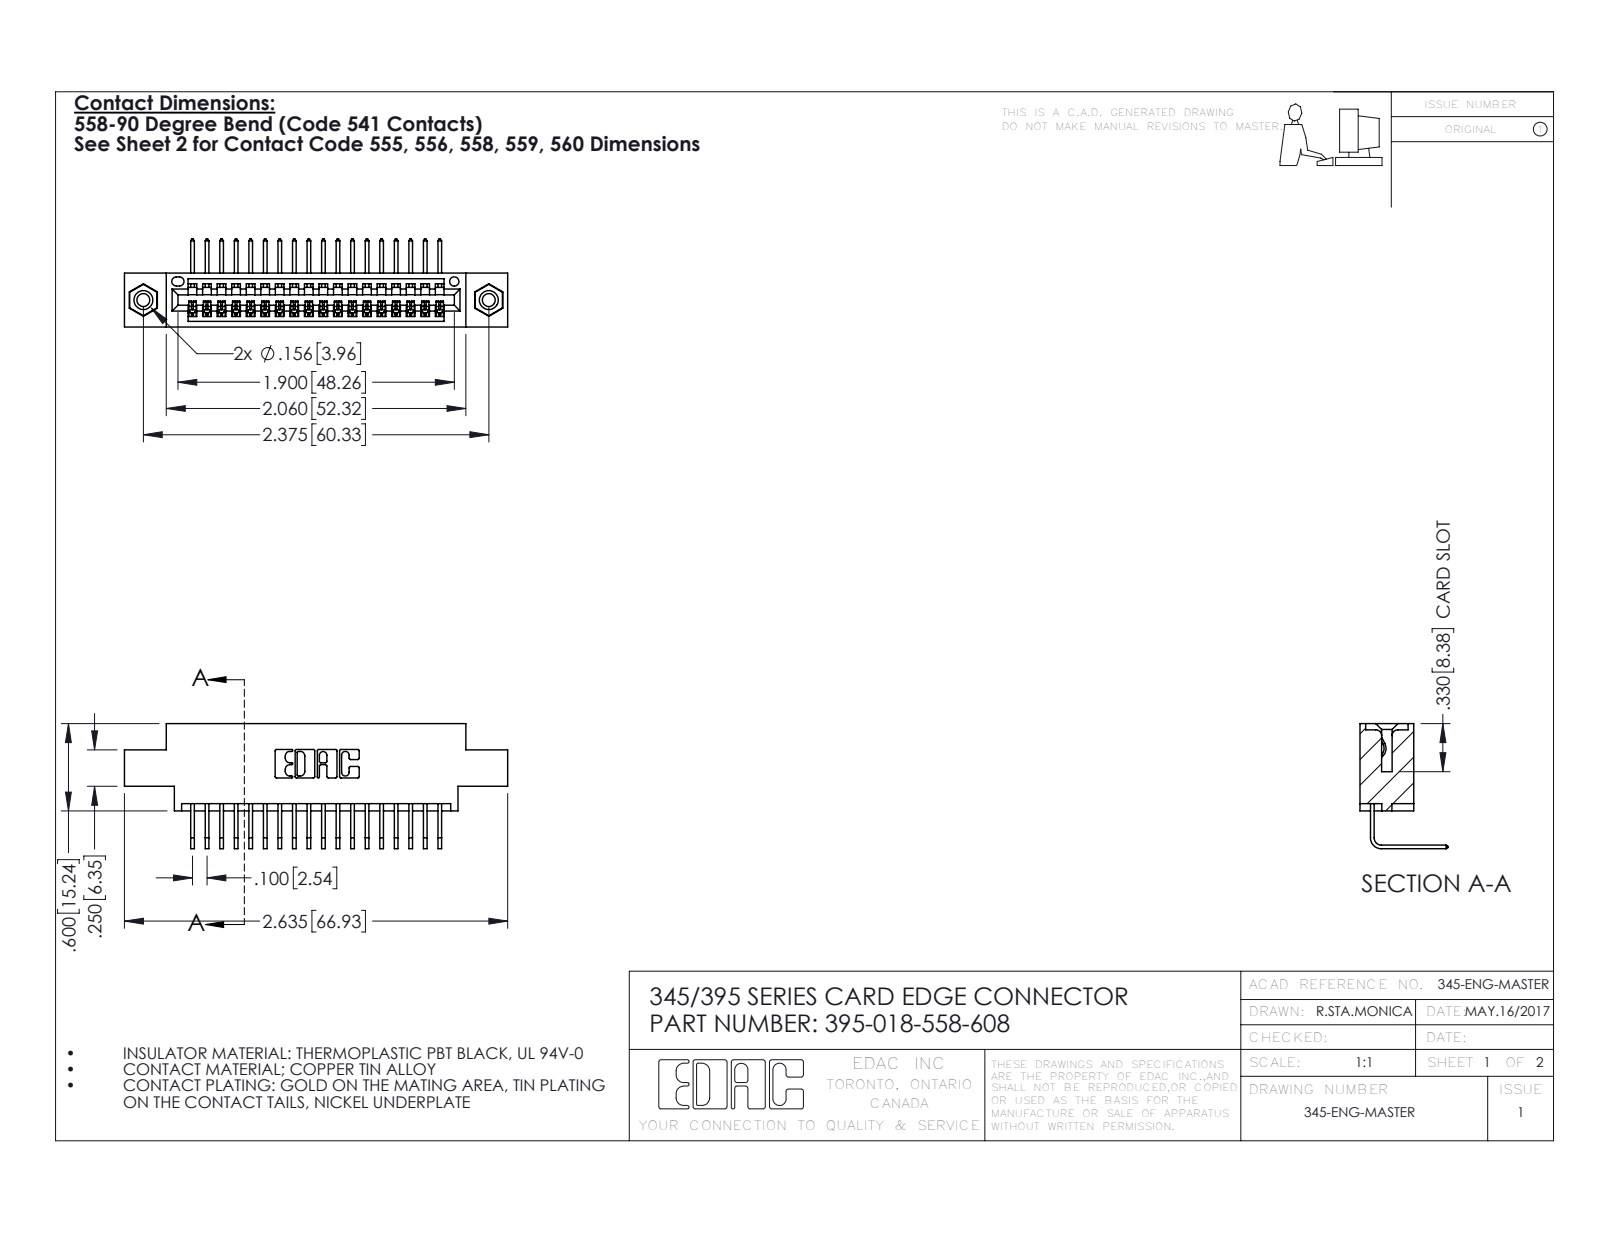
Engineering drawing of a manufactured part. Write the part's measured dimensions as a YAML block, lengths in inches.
part_name: "345 Part_0.170 Offset - 0.156 Dia-TI; 345-250-001_345-250-003-102; 395-018-558-608; 345-292-001_558 Tail - 2"
step_written_by: "SolidWorks 2016 (CONFIG_CONTROL_DESIGN)"
units: inches
bodies: {solids: 21, faces: 1270, planar: 872, cylindrical: 382, other: 16}
overall_size: [2.635, 0.859, 0.605]
volume: 0.372
surface_area: 12.83
round_holes:
  - {diameter: 0.089, count: 2}
  - {diameter: 0.125, count: 2}
  - {diameter: 0.156, count: 2}
  - {diameter: 0.064, count: 1}
round_bosses_or_shafts:
  - {diameter: 0.155, count: 2}
partial_cylinders:
  - {radius: 0.006, count: 36}
  - {radius: 0.01, count: 22}
  - {radius: 0.007, count: 6}
  - {radius: 0.031, count: 6}
  - {radius: 0.026, count: 3}
  - {radius: 0.031, count: 2}
  - {radius: 0.04, count: 2}
  - {radius: 0.014, count: 1}
face_to_face_distances: [0.072, 0.298, 0.37, 0.2, 0.098, 0.272, 0.025, 0.225, 0.1, 0.15]
hole_center_spacings: [0.27, 2.141, 2.375]
